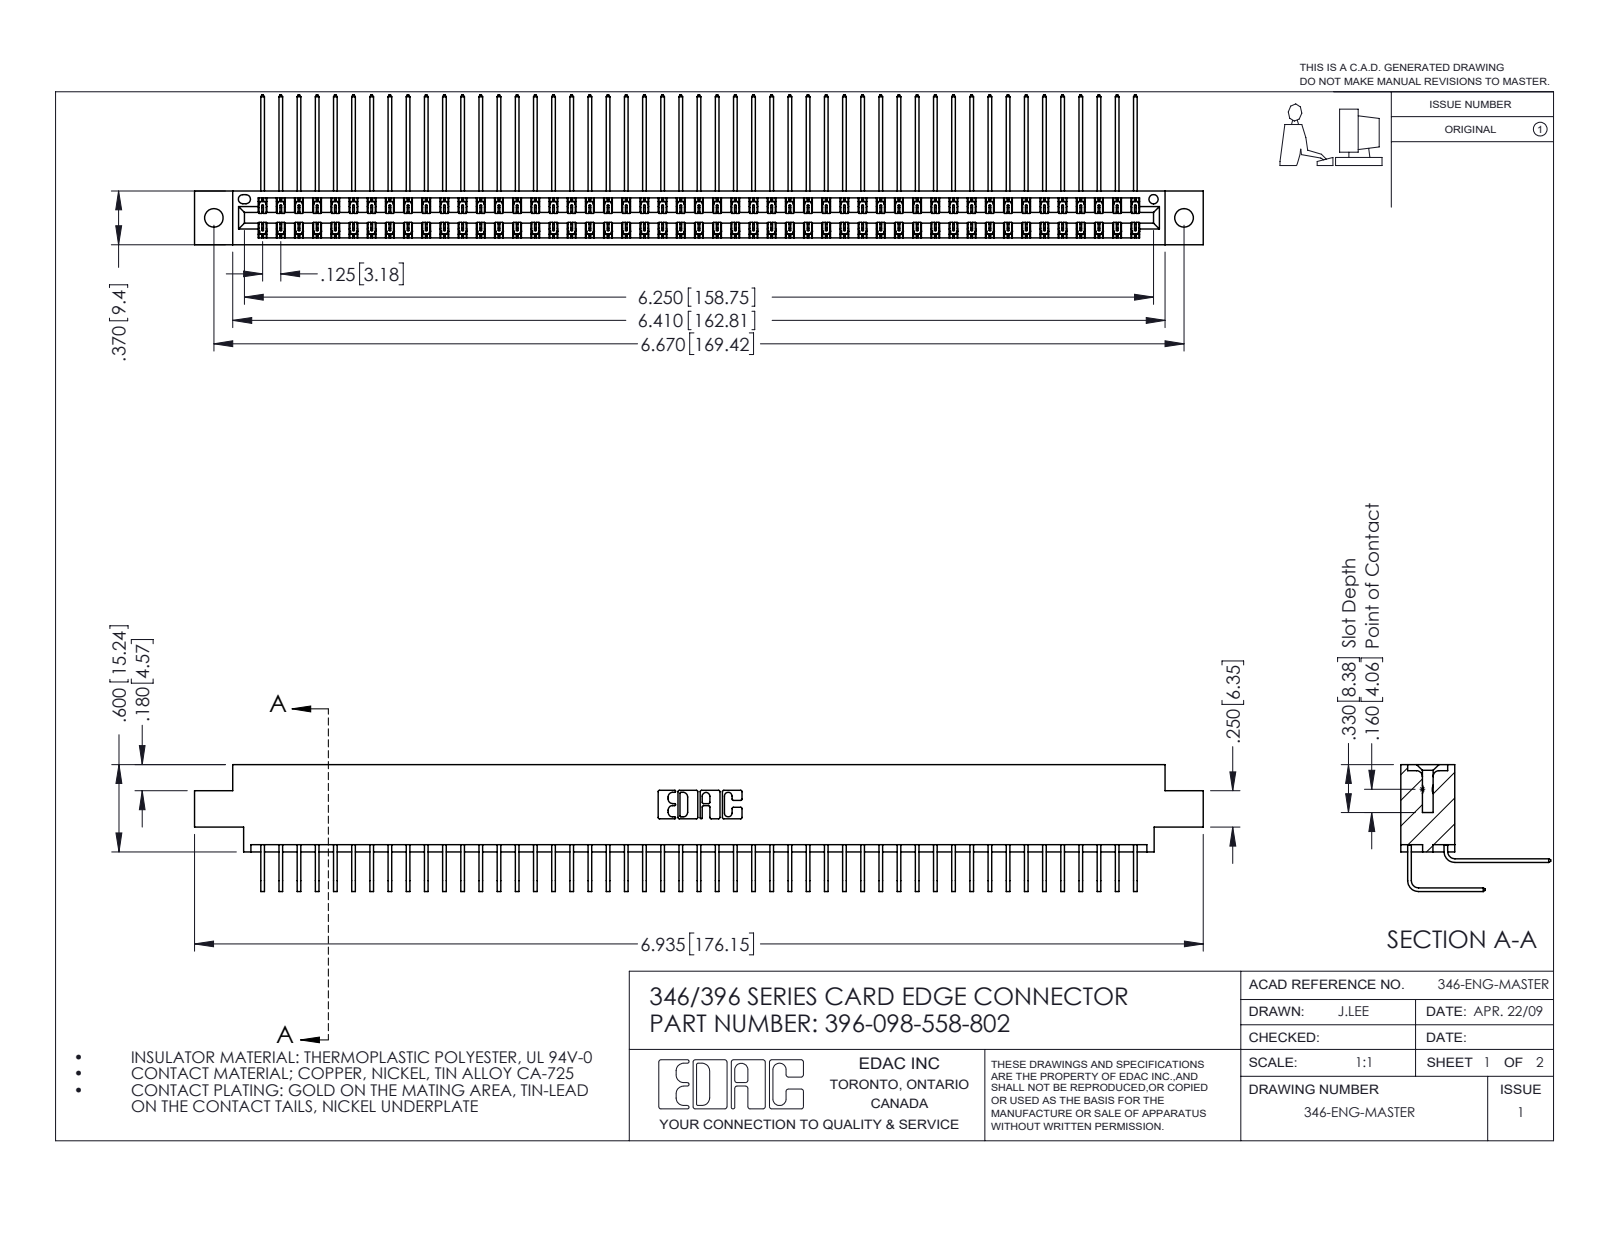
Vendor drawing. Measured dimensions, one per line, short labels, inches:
name: 345-292-001_558 Tail - 2; 345-292-001_558 559 Tail - 1; 346 Part_0.170 Offset - 0.128 Dia; 396-098-558-802
written by: SolidWorks 2016 (CONFIG_CONTROL_DESIGN)
unit: in
bodies: 99 solids, 5418 faces (3706 planar, 1712 cylindrical, 0 other)
size: 6.935 × 1.03 × 0.873
volume: 1.074 in³; area: 41.74 in²
holes: 2× ⌀0.128, 1× ⌀0.064
rounds: 147× R0.006, 22× R0.01, 6× R0.007, 6× R0.031, 3× R0.026, 2× R0.014, 2× R0.022, 2× R0.024
face distances: 0.322, 0.048, 0.025, 0.37, 0.25, 0.298, 0.072, 0.275, 0.148, 0.222
hole spacings: 0.246, 6.461, 6.67
